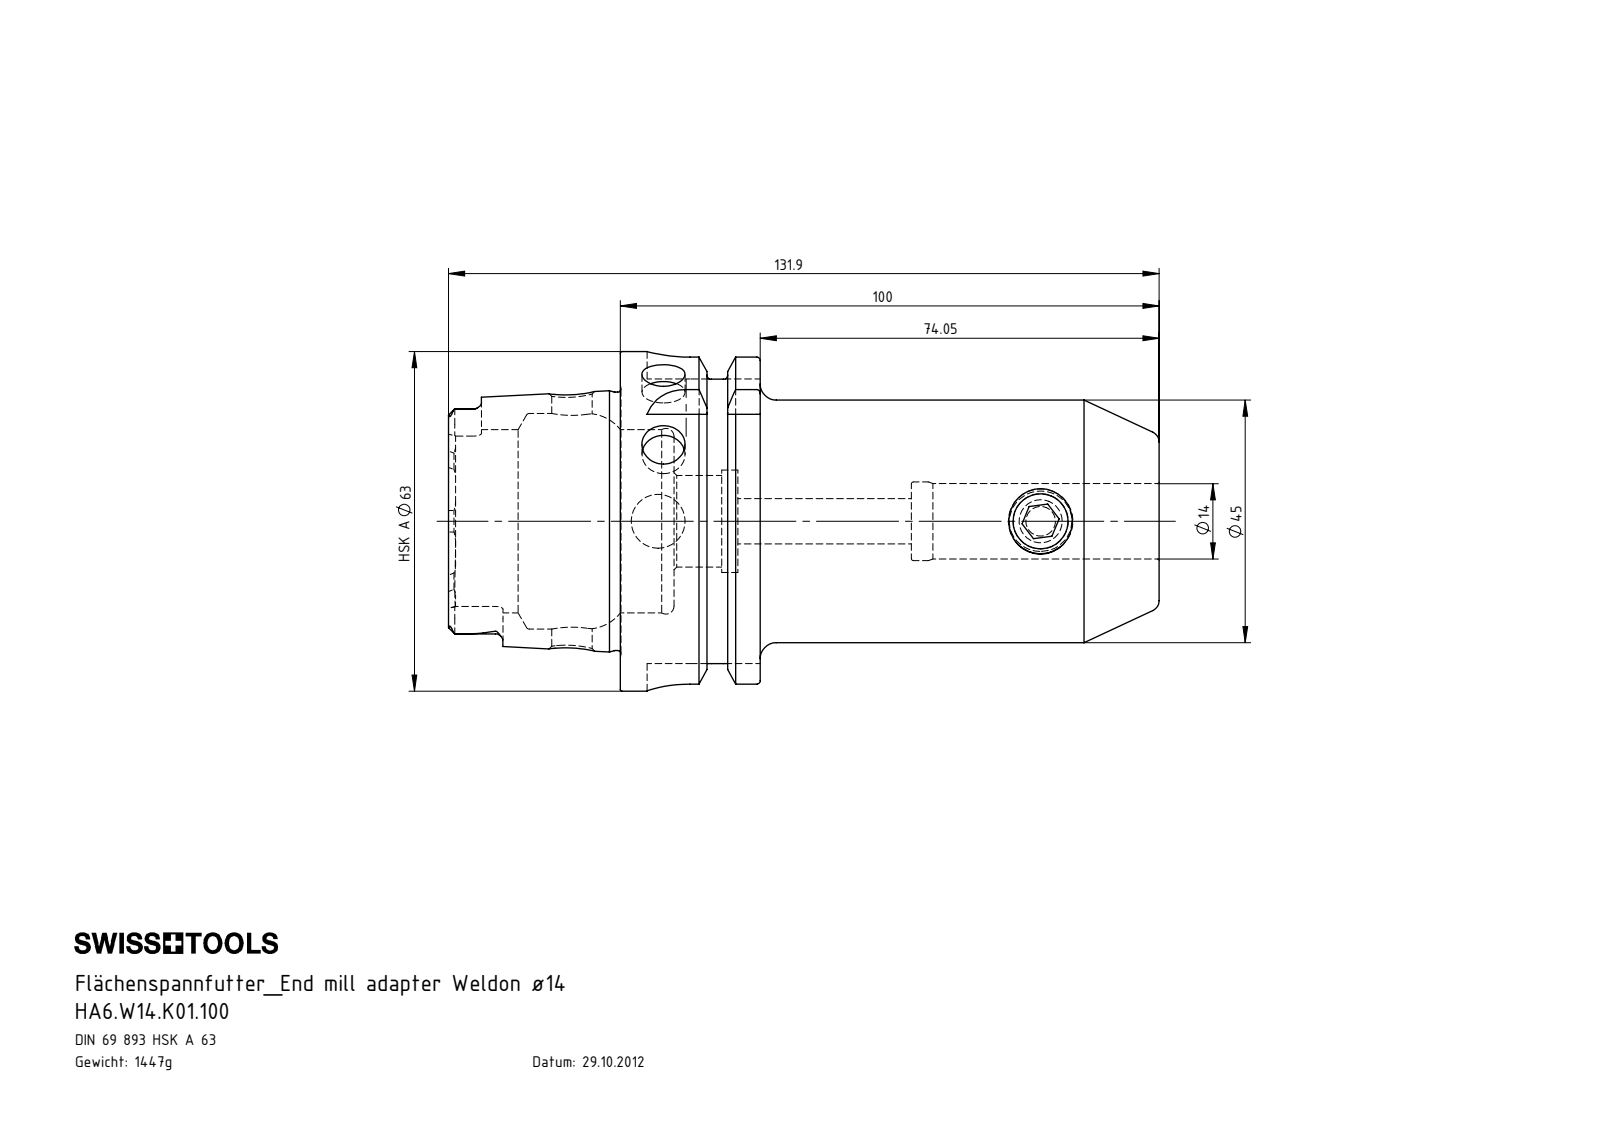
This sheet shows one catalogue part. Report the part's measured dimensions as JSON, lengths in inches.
{"part_name": "HA6-W14.K01.100; HA6-W14.K01.100_A_Fertigbearbeitung; W12-ER1.001.016", "step_written_by": "SolidWorks 2012 (CONFIG_CONTROL_DESIGN)", "units": "inches", "bodies": {"solids": 2, "faces": 208, "planar": 58, "cylindrical": 57, "other": 93}, "overall_size": [5.193, 2.48, 2.48], "volume_in3": 11.25, "surface_area_in2": 55.62, "round_holes": [[0.315, 2], [0.295, 1], [0.331, 1], [0.394, 1], [0.404, 1], [0.551, 1], [0.575, 1], [0.669, 1], [0.748, 1], [1.339, 1], [1.575, 1]], "round_bosses_or_shafts": [[2.48, 1], [2.163, 1], [1.887, 1], [1.772, 1], [0.472, 1]], "partial_cylinders_radius": [[0.055, 6], [0.113, 4], [0.315, 4]], "face_to_face_distances": [1.022, 0.63, 0.392, 3.937, 3.545, 2.915, 1.256, 1.648, 2.278, 5.193], "hole_center_spacings": [2.795]}
